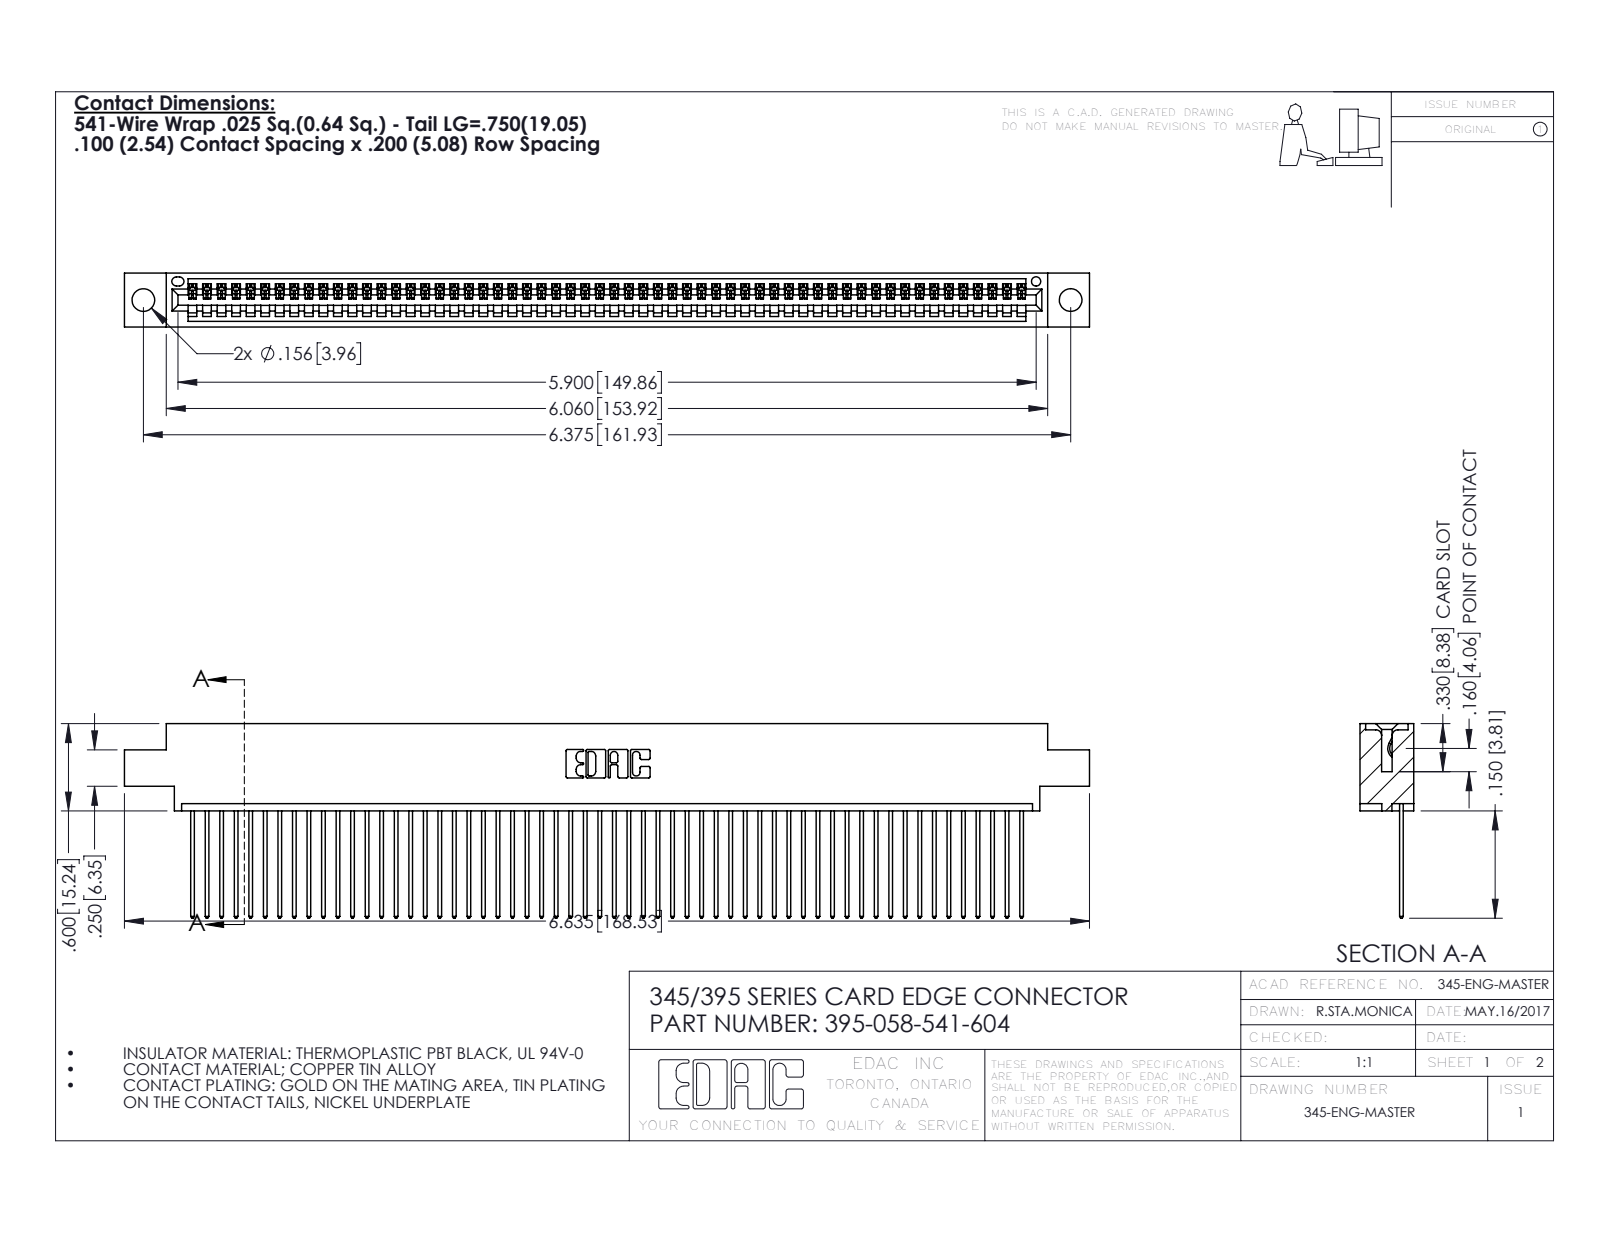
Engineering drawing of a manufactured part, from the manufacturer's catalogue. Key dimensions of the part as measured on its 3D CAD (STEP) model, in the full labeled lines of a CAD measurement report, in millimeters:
Part name (STEP PRODUCT): 345-292-001_345-293-141; 395-058-541-604; 345 Part_0.170 Offset - 0.156 Dia-TH
STEP written by: SolidWorks 2016 (CONFIG_CONTROL_DESIGN)
Units: millimetres
Bodies: 59 solids, 3494 faces (2404 planar, 1090 cylindrical, 0 other)
Overall size (bounding box): 168.5 × 34 × 9.4
Volume: 16 100 mm³ · Surface area: 22 710 mm²
Round holes (diameter × count): ⌀4 ×2, ⌀1.6 ×1
Partial cylindrical surfaces — rounded edges, fillets, slot ends (radius × count): R0.2 ×116, R0.3 ×116, R0.3 ×22, R0.2 ×6, R0.8 ×6, R0.7 ×3, R0.8 ×2, R1 ×2
Main face-to-face distances: 1.8, 7.6, 2.5, 6.9, 0.6, 9.4, 5.1, 5.7, 4.4, 3.8
Hole centre spacings: 6.9, 155.9, 161.9
